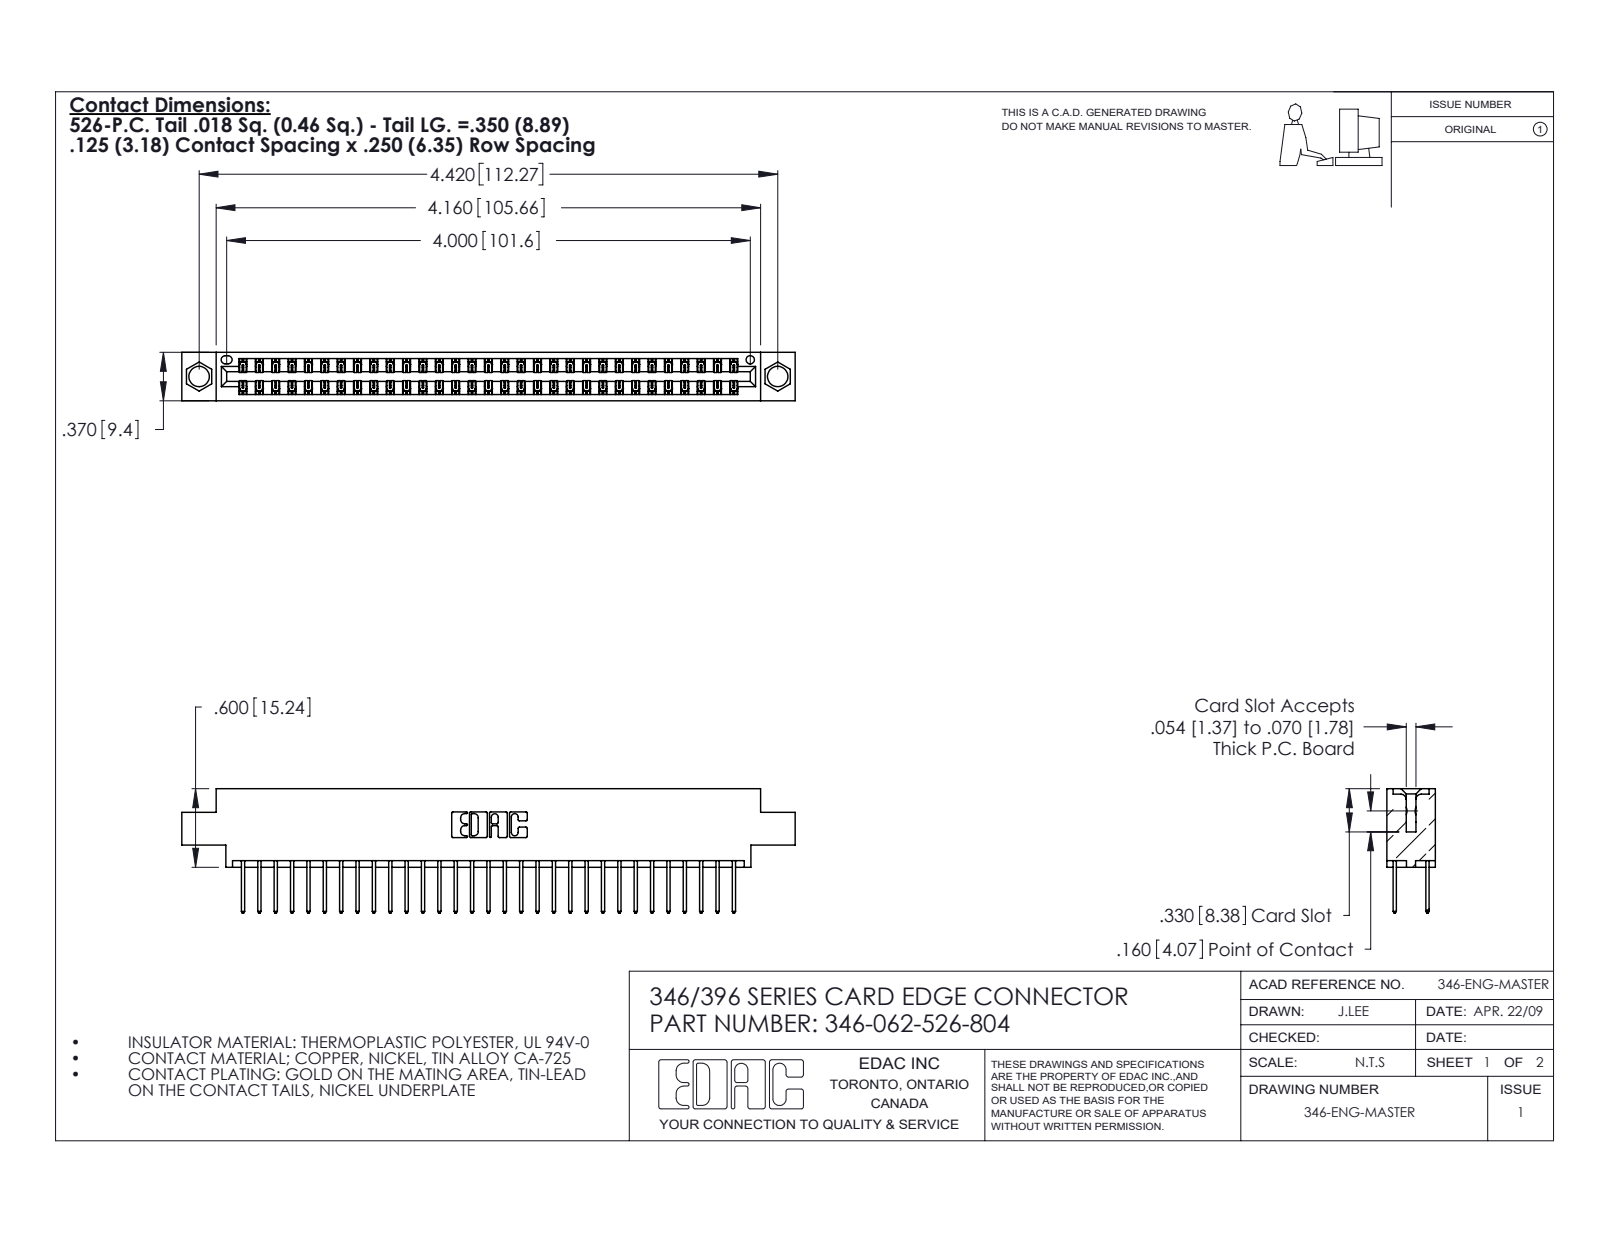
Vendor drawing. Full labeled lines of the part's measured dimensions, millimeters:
Part name (STEP PRODUCT): 346 Part_0.170 Offset - 0.156 Dia-TH; 345-292-001_345-293-126; 346-062-526-804
STEP written by: SolidWorks 2020 (CONFIG_CONTROL_DESIGN)
Units: millimetres
Bodies: 63 solids, 3364 faces (2264 planar, 1100 cylindrical, 0 other)
Overall size (bounding box): 119 × 24.1 × 9.4
Volume: 11 400 mm³ · Surface area: 15 920 mm²
Round holes (diameter × count): ⌀4 ×2, ⌀1.6 ×1
Partial cylindrical surfaces — rounded edges, fillets, slot ends (radius × count): R0.2 ×93, R0.3 ×62, R0.3 ×22, R0.2 ×6, R0.8 ×6, R0.7 ×3, R0.4 ×2, R0.6 ×2
Main face-to-face distances: 1.2, 8.2, 6.4, 9.4, 1.8, 7.6, 0.6, 7, 5.6, 3.8
Hole centre spacings: 6.2, 107, 112.3
